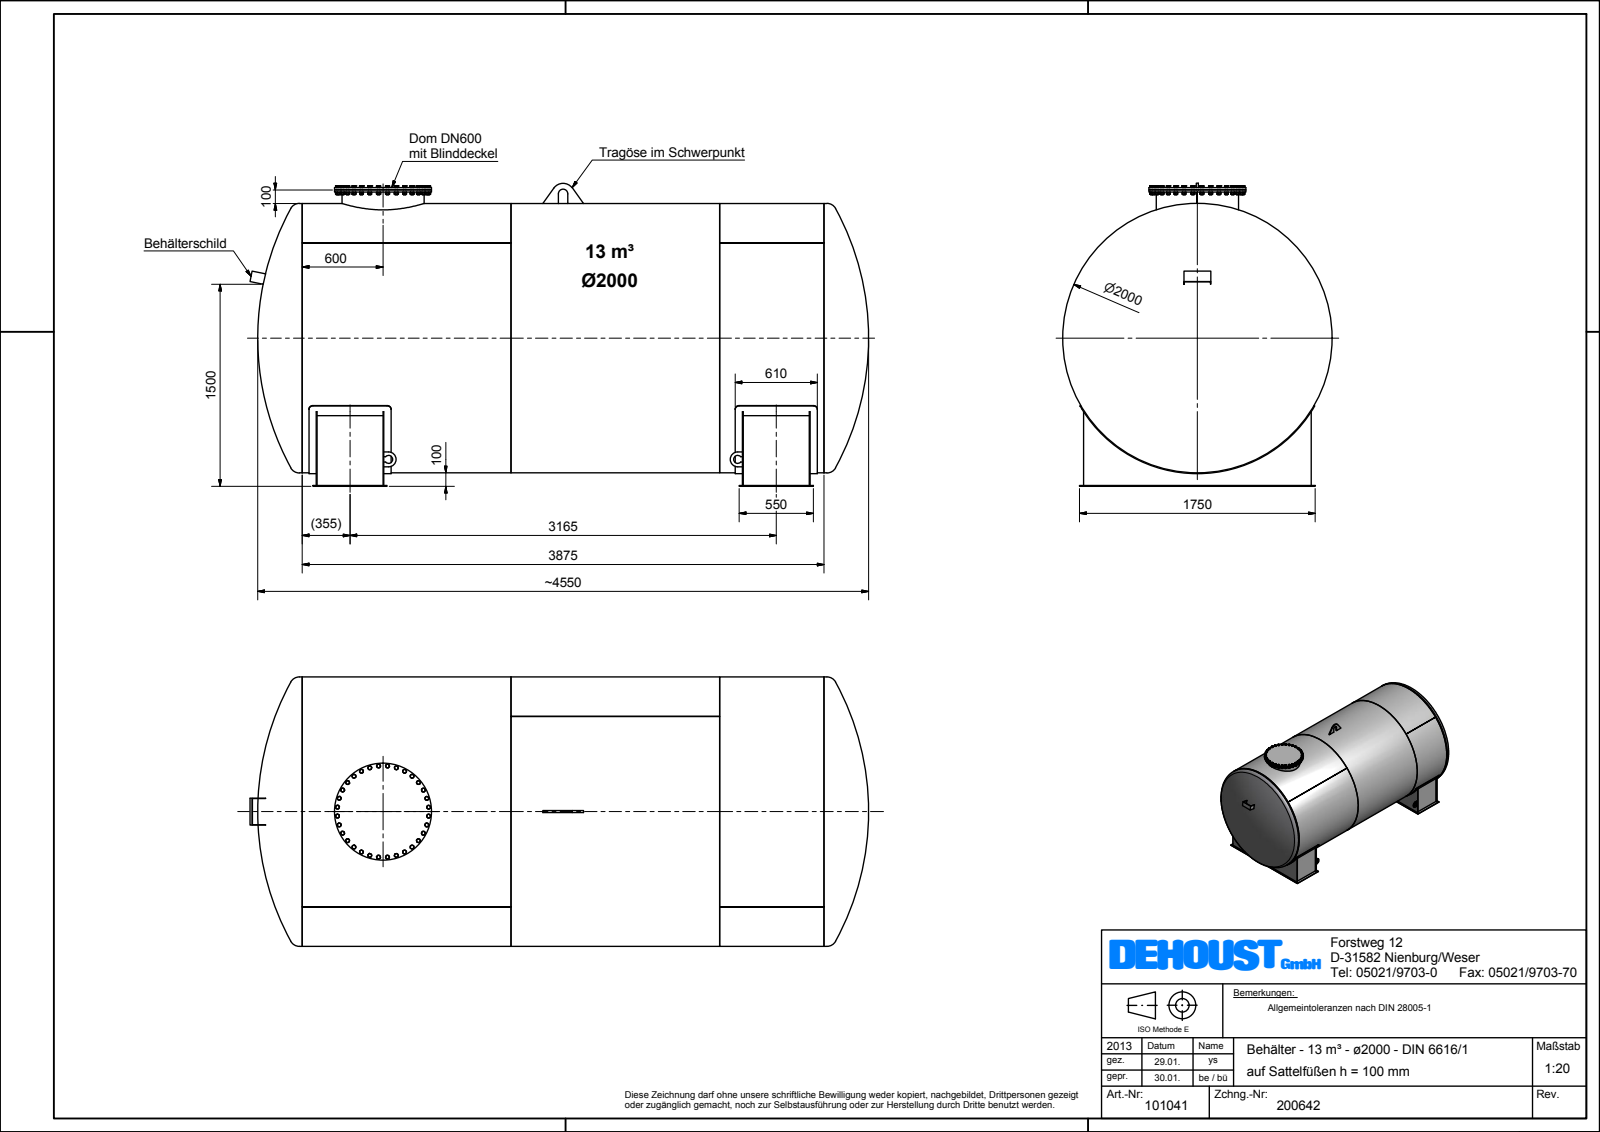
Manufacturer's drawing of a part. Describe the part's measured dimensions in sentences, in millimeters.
The part is named "Beh\\S\\dlter_6616_E_2000_013_100_KV". Its 3-D file was written by "Autodesk Inventor 2012 (AUTOMOTIVE_DESIGN)". It is 3 solids with 1115 faces: 660 planar, 163 cylindrical and 292 other. Overall it measures 4593.87 by 2250 by 2000 millimeters. Its volume is 1 458 000 000 cubic millimeters and its surface area 72 830 000 square millimeters. Round holes: 1 of diameter 598, 1 of diameter 1988. Round bosses or shafts: 32 of diameter 24.8, 32 of diameter 18, 32 of diameter 16.65, 1 of diameter 2000, 1 of diameter 720, 1 of diameter 660, 1 of diameter 610. Partial cylindrical surfaces (rounded edges, fillets, slot ends): 8 of radius 30, 2 of radius 29.73, 2 of radius 55, 1 of radius 35, 1 of radius 85, 1 of radius 1006. The main face-to-face distances are 6, 3875, 3165, 496, 1644, 104, 3771, 606, 3269, 502.
